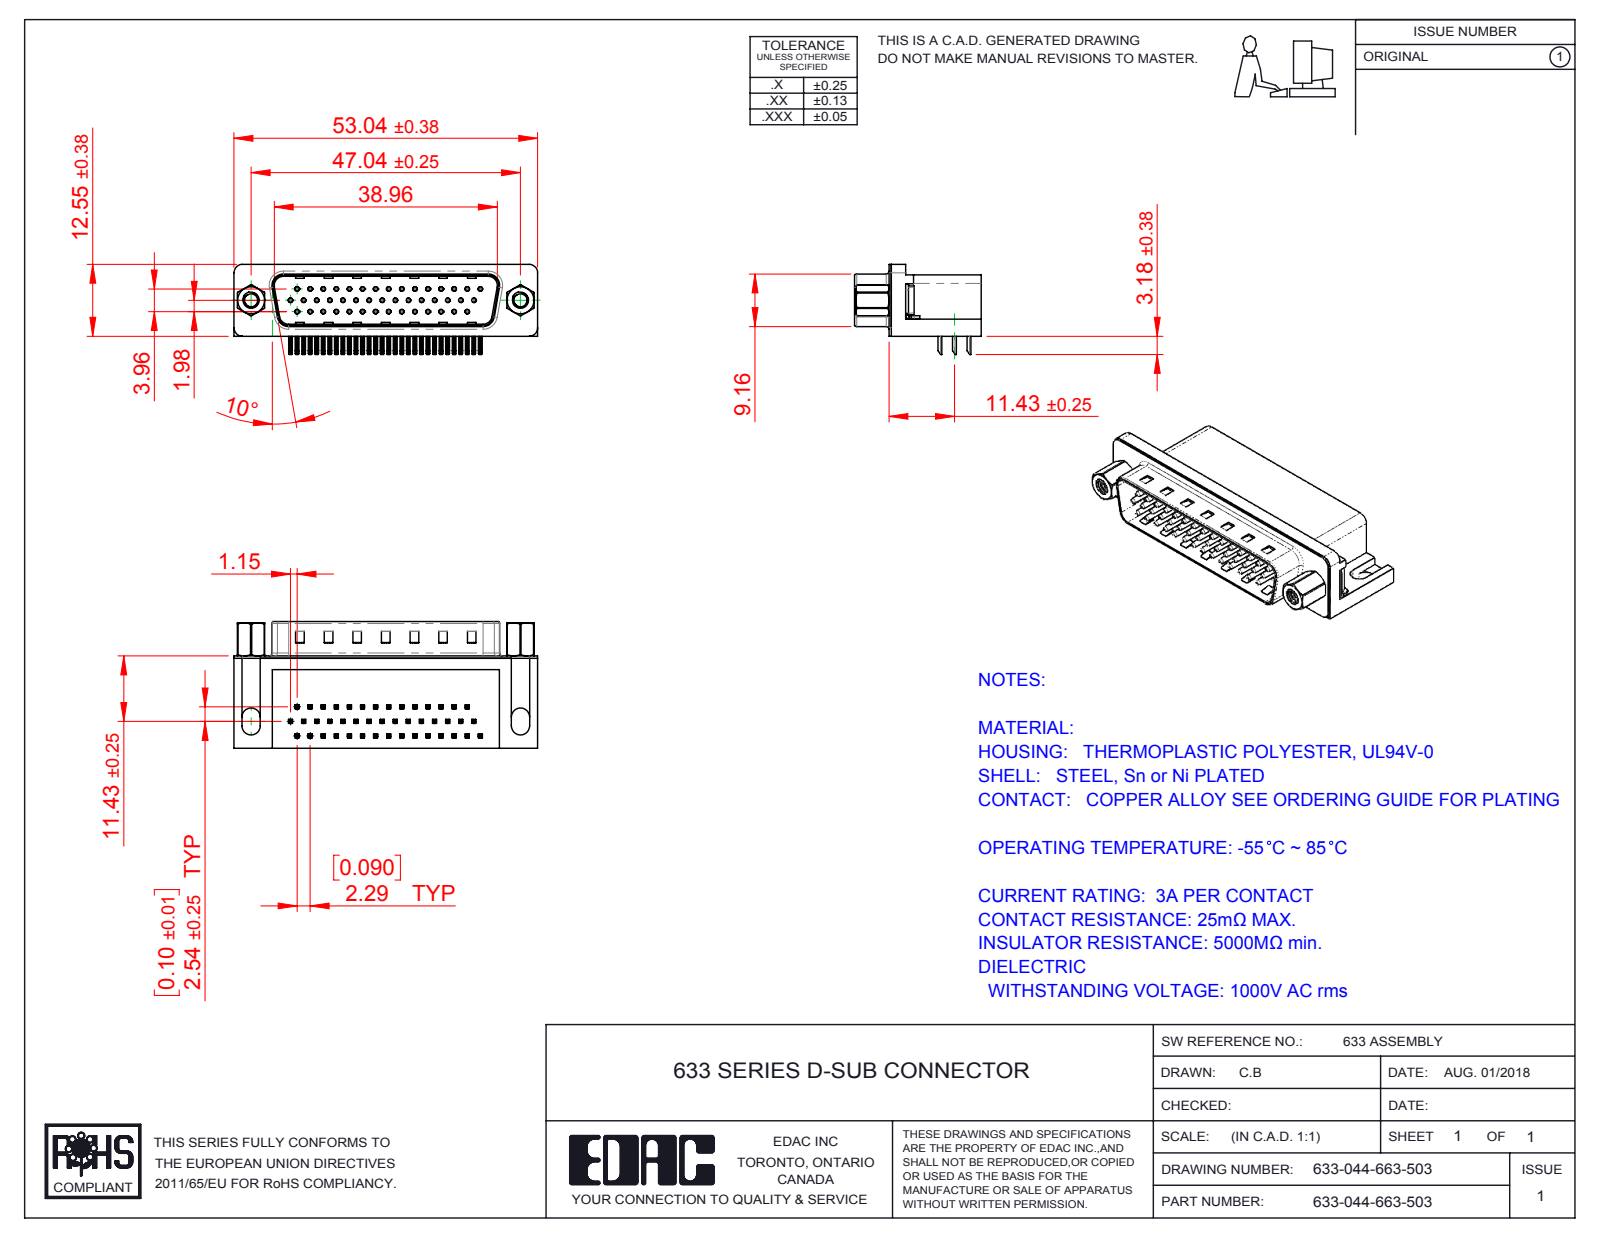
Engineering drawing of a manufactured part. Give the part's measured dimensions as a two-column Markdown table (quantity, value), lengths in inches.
| quantity | value |
| --- | --- |
| part name | 633 Contact Bottom; 633 Shell_44 Contact; 633 Non Board Mount; 633 4-40 Threaded Rivet (+5 more) |
| STEP written by | SolidWorks 2016 (CONFIG_CONTROL_DESIGN) |
| units | inches |
| bodies | 52 solids, 3806 faces (2339 planar, 1120 cylindrical, 347 other) |
| overall size | 2.088 × 0.87 × 0.619 |
| volume | 0.505 in³ |
| surface area | 16.19 in² |
| round holes (diameter × count) | 0.014 × 44, 0.031 × 44, 0.089 × 2, 0.09 × 2, 0.157 × 2, 0.189 × 2, 0.197 × 2 |
| round bosses / shafts (diameter × count) | 0.03 × 44, 0.193 × 2, 0.187 × 2, 0.154 × 2, 0.11 × 2 |
| partial cylindrical surfaces (radius × count) | 0.01 × 184, 0.005 × 88, 0.039 × 16, 0.02 × 9, 0.063 × 8, 0.059 × 7, 0.035 × 4, 0.079 × 4 |
| main face-to-face distances | 0.016, 0.407, 0.618, 0.345, 0.114, 0.098, 0.634, 0.083, 0.421, 0.1 |
| hole center spacings | 0.09, 0.18, 0.18, 0.09, 0.27, 0.361, 0.451, 0.089 |
